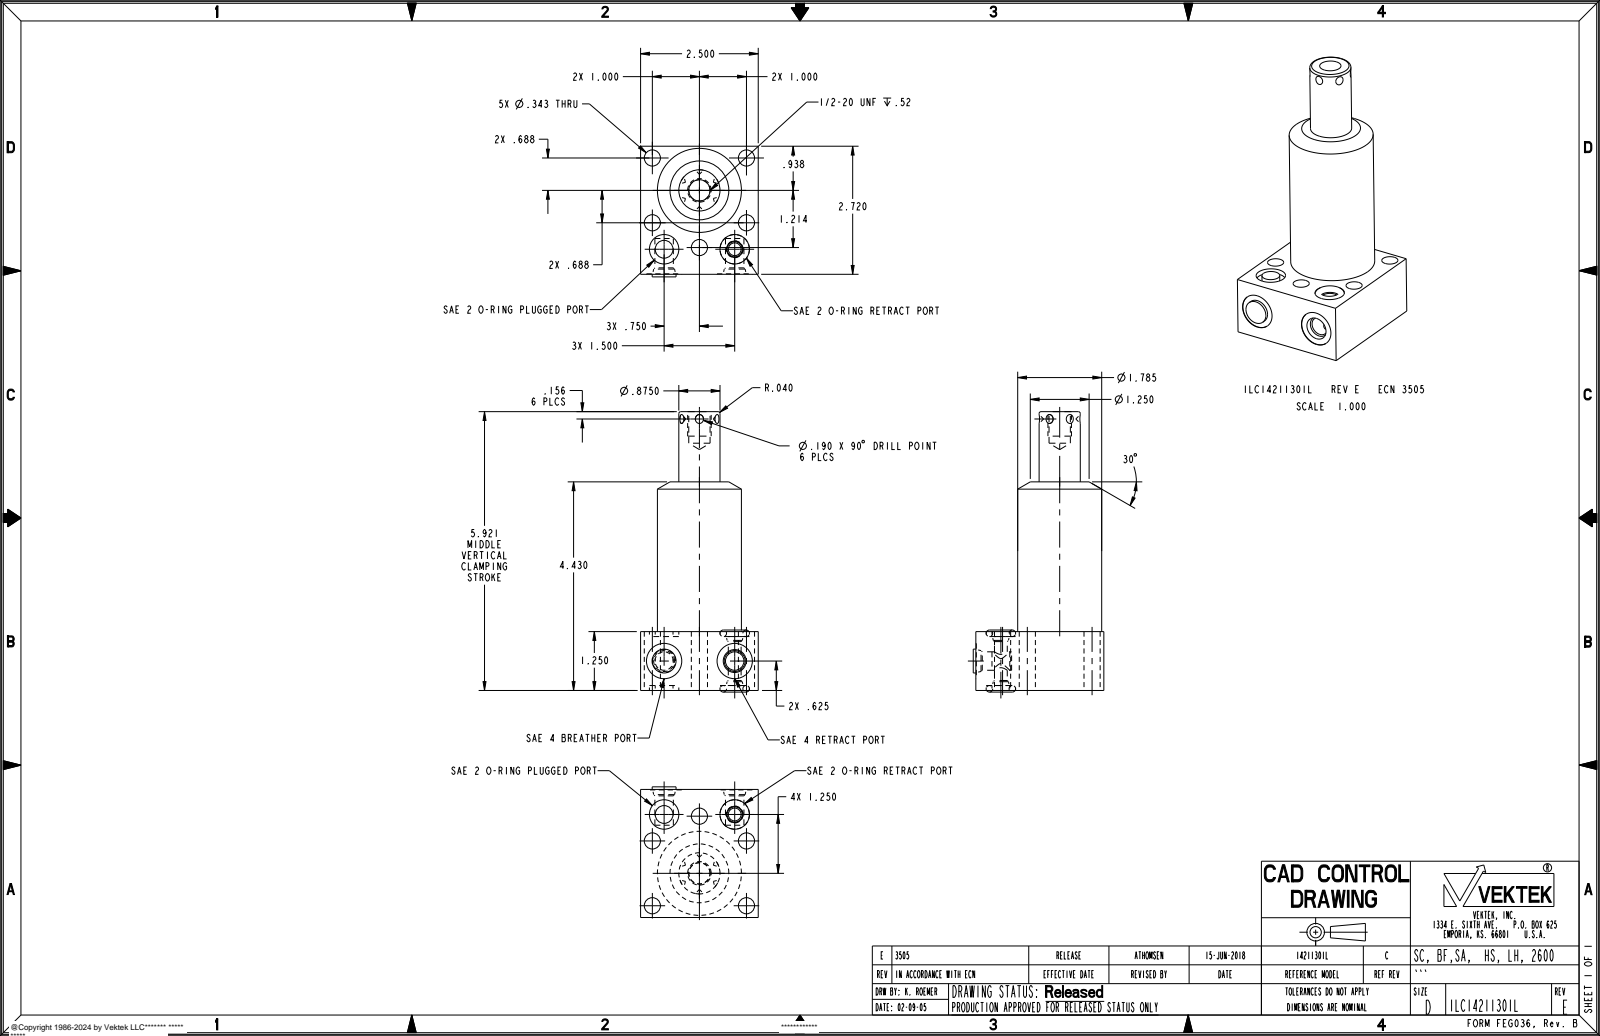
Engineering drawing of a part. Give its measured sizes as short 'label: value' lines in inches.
name: ILC14211301L
written by: PRO/ENGINEER BY PARAMETRIC TECHNOLOGY CORPORATION, 2013320 (AUTOMOTIVE_DESIGN)
unit: in
bodies: 3 solids, 109 faces (21 planar, 46 cylindrical, 42 other)
size: 5.955 × 2.775 × 2.5
volume: 16.3 in³; area: 60.69 in²
holes: 5× ⌀0.343, 2× ⌀0.392, 2× ⌀0.625, 2× ⌀0.75, 1× ⌀0.272, 1× ⌀0.453
bosses: 1× ⌀1.785, 1× ⌀0.875, 1× ⌀0.507, 1× ⌀0.5, 1× ⌀0.378
face distances: 2.5, 1.25, 2.72, 0.105, 1.145, 2.71, 4.43, 3.18, 1.04, 4.325
hole spacings: 1.214, 0.615, 0.751, 1.13, 1.376, 1.458, 1.5, 1.838
